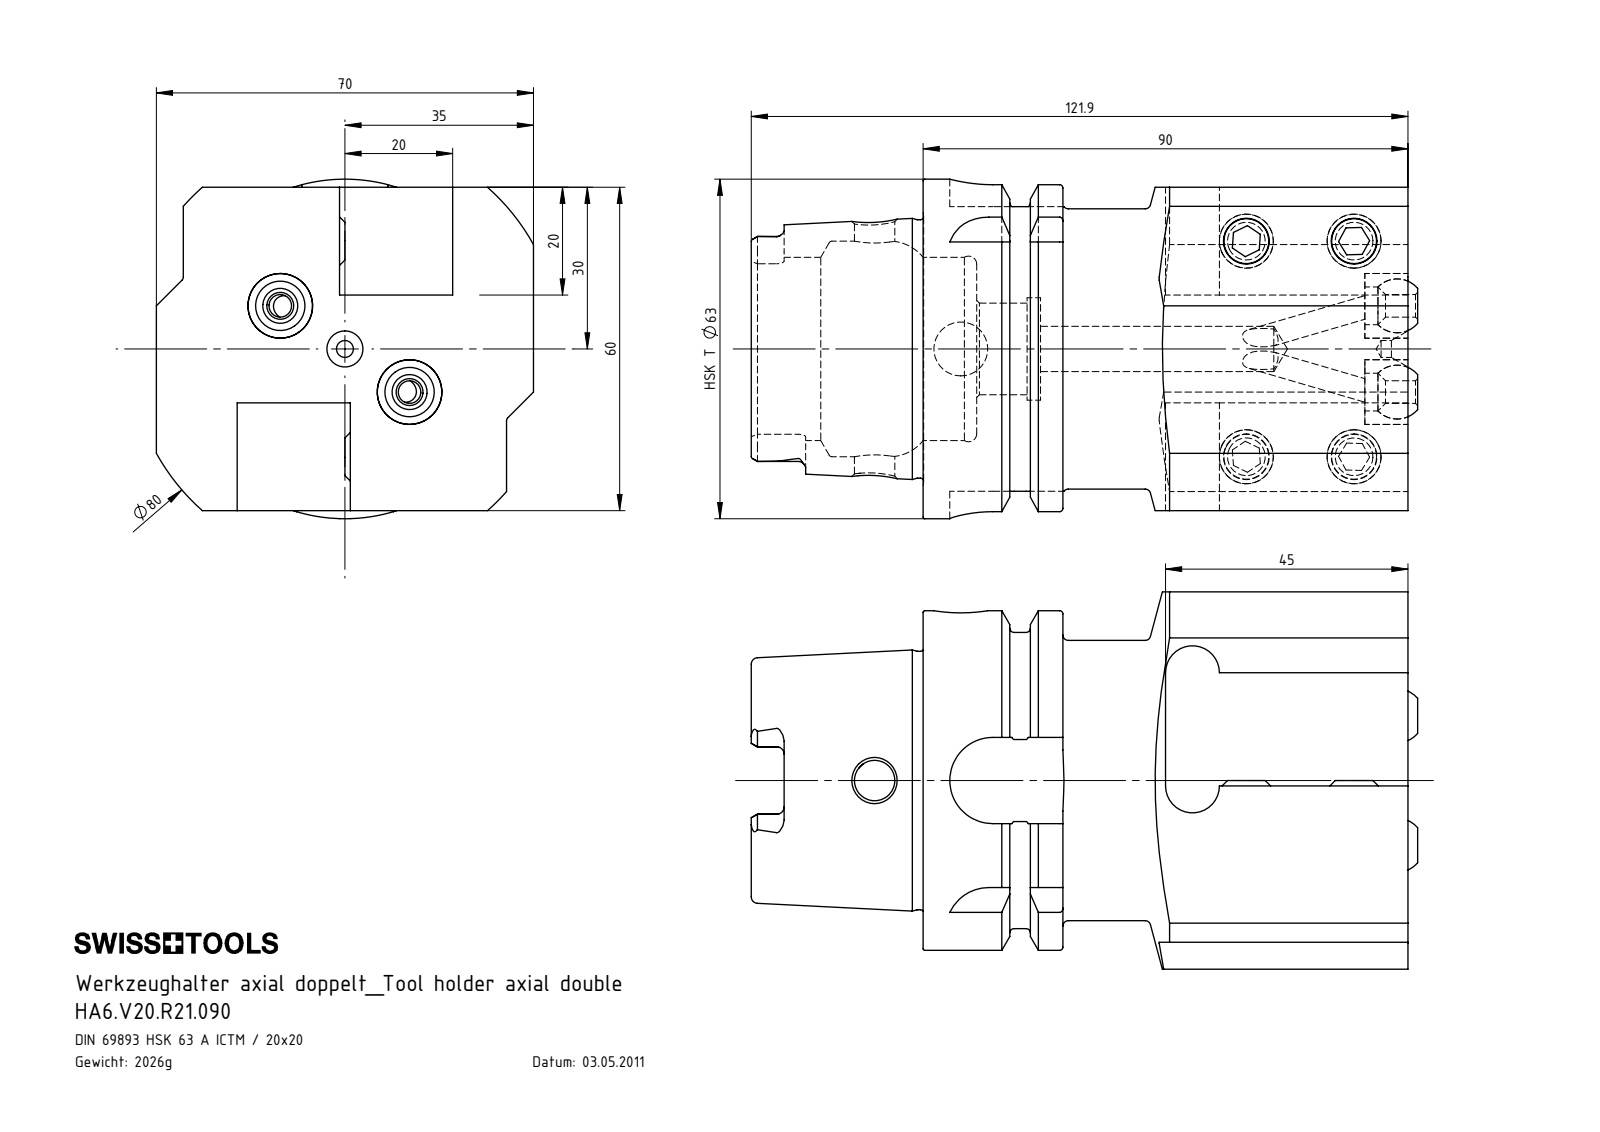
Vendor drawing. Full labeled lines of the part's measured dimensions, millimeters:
Part name (STEP PRODUCT): KU1-U12.001.010_2; KU1-U12.001.010_1; ISO 4026 - M10 x 30; HA6-V20.R21.090_B (+2 more)
STEP written by: SolidWorks 2017 (AUTOMOTIVE_DESIGN)
Units: millimetres
Bodies: 9 solids, 306 faces (103 planar, 94 cylindrical, 109 other)
Overall size (bounding box): 123.7 × 70 × 63
Volume: 258 658 mm³ · Surface area: 54 862 mm²
Round holes (diameter × count): ⌀4.2 ×4, ⌀8.5 ×4, ⌀7 ×2, ⌀12 ×2, ⌀3.15 ×1, ⌀7.5 ×1, ⌀8.4 ×1, ⌀10 ×1, ⌀17 ×1, ⌀19 ×1, ⌀34 ×1, ⌀40 ×1
Round bosses / shafts (diameter × count): ⌀10 ×4, ⌀63 ×1, ⌀54.95 ×1, ⌀52 ×1, ⌀47.94 ×1
Partial cylindrical surfaces — rounded edges, fillets, slot ends (radius × count): R1.4 ×6, R2.88 ×4, R5 ×4, R8 ×4, R0.8 ×2, R40 ×1
Main face-to-face distances: 20, 40, 60, 45, 15, 55, 5, 70, 10, 21
Hole centre spacings: 14.42, 20, 40, 44.72, 56.65, 75.69, 28.84
